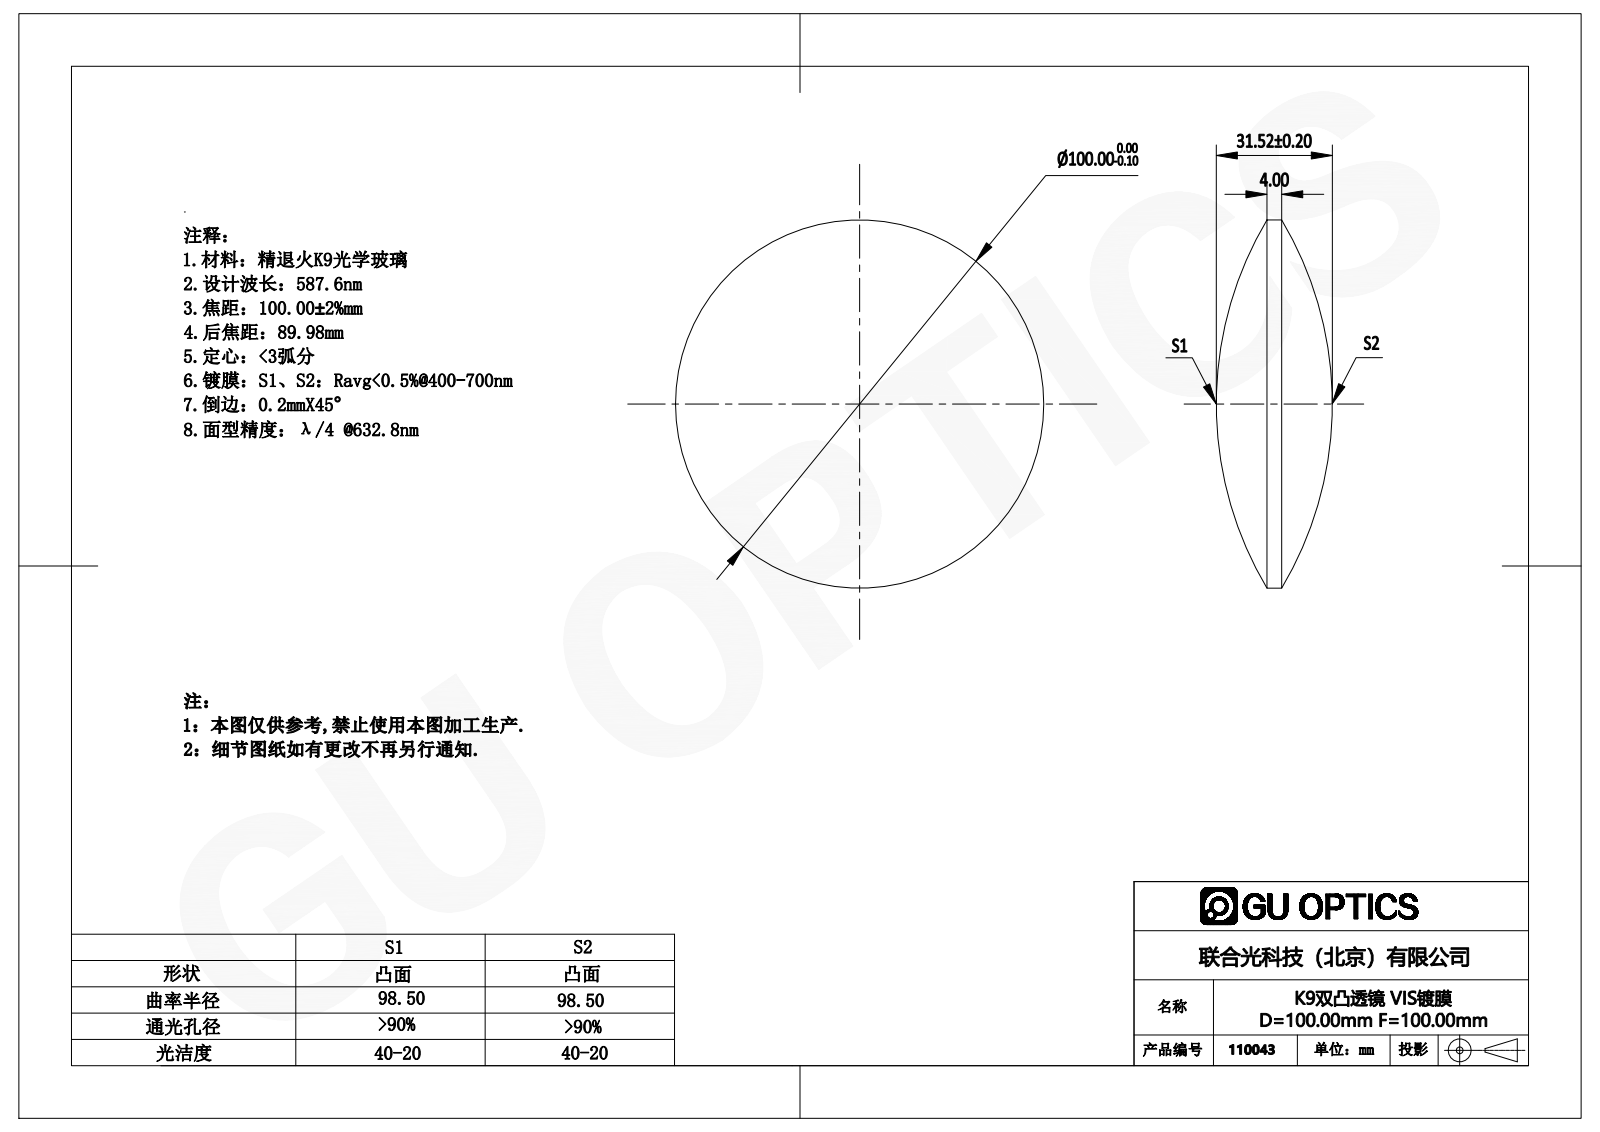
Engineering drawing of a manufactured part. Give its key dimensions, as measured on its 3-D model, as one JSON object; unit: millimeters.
{"part_name": "110021", "step_written_by": "SolidWorks 2016 (CONFIG_CONTROL_DESIGN)", "units": "millimeters", "bodies": {"solids": 1, "faces": 6, "planar": 0, "cylindrical": 2, "other": 4}, "overall_size": [100, 100, 31.52], "volume_mm3": 142215, "surface_area_mm2": 18154, "round_bosses_or_shafts": [[100, 1]]}
